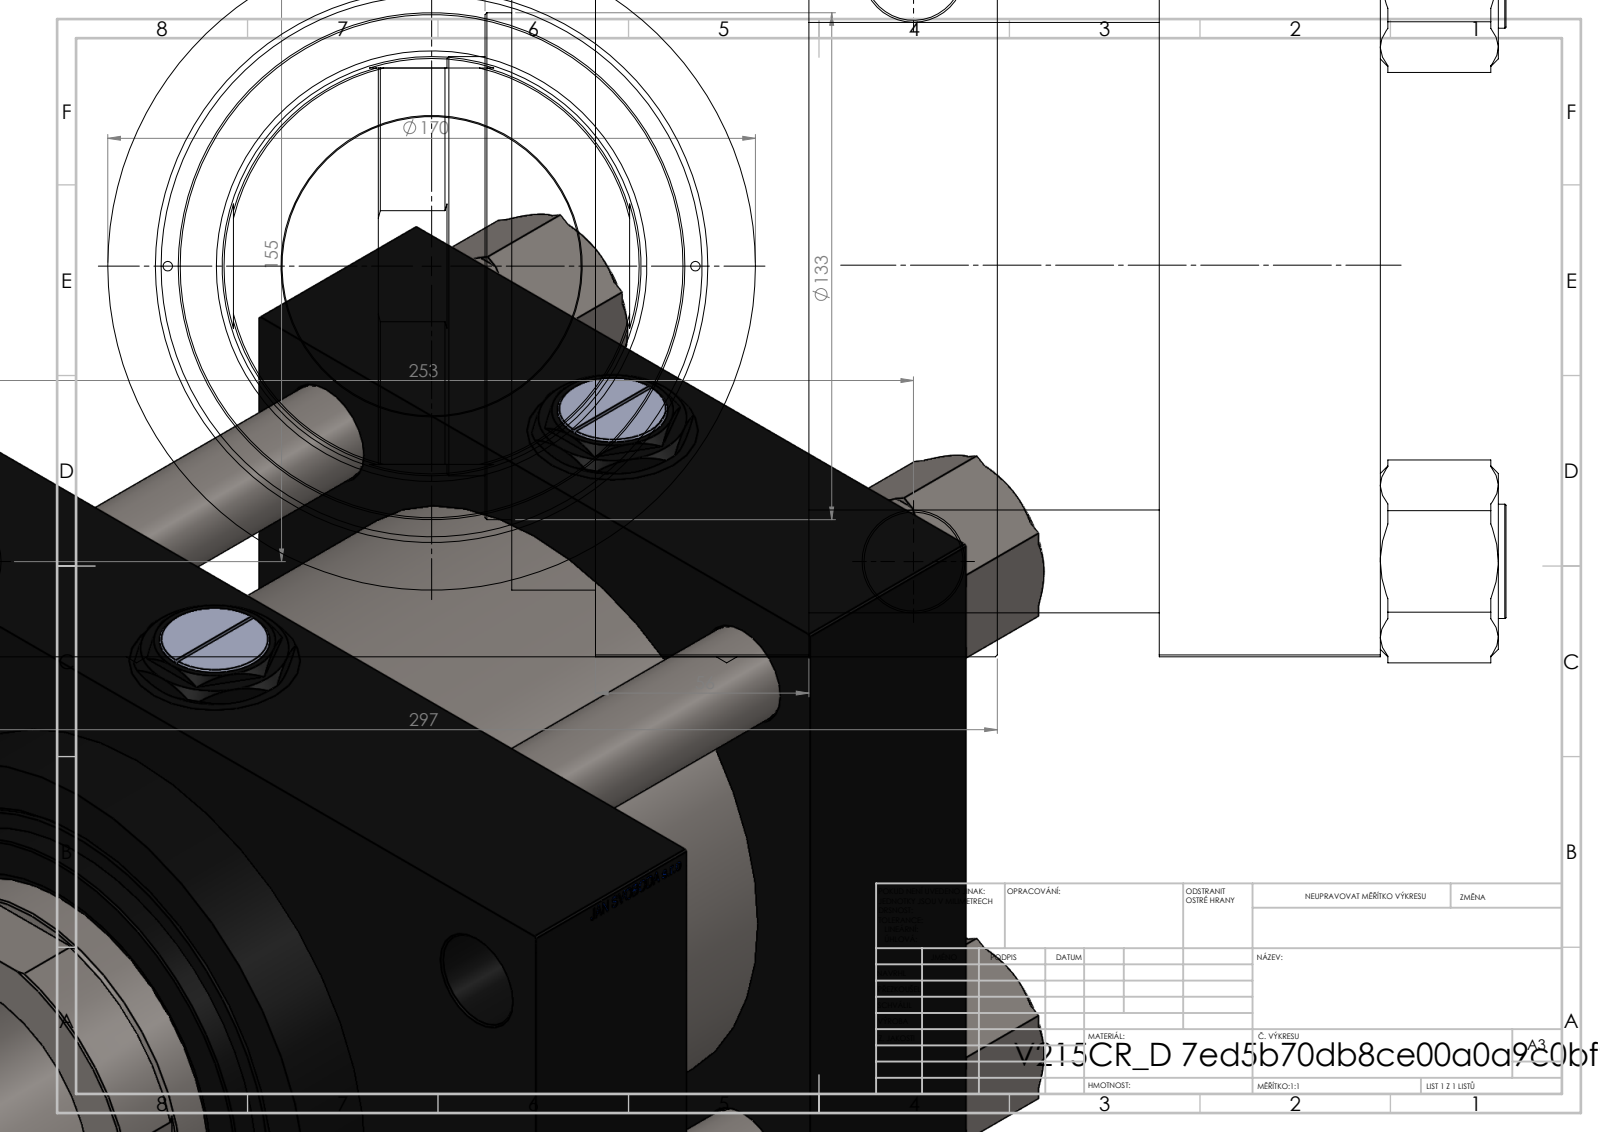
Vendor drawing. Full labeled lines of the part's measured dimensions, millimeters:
Part name (STEP PRODUCT): V215_VC_A; Zatka_pro_OIL_PORT; NUT_M5_D; V215CR_D_Body (+2 more)
STEP written by: SolidWorks 2019 (CONFIG_CONTROL_DESIGN)
Units: millimetres
Bodies: 13 solids, 1260 faces (595 planar, 103 cylindrical, 562 other)
Overall size (bounding box): 297 × 296 × 213.57
Volume: 8 094 000 mm³ · Surface area: 790 615 mm²
Round holes (diameter × count): ⌀26 ×4, ⌀27 ×4, ⌀33.24 ×4, ⌀45 ×4, ⌀7 ×3, ⌀2.5 ×2, ⌀78.5 ×1, ⌀110 ×1, ⌀113 ×1, ⌀120 ×1, ⌀142 ×1, ⌀160 ×1
Round bosses / shafts (diameter × count): ⌀30 ×4, ⌀170 ×1, ⌀166 ×1, ⌀133 ×1
Partial cylindrical surfaces — rounded edges, fillets, slot ends (radius × count): R54 ×1
Main face-to-face distances: 58, 150, 92, 205, 148, 56, 206, 46, 251, 72
Hole centre spacings: 49.05, 77.88, 96.35, 109.53, 148.35, 154.9, 162.53, 165.89
